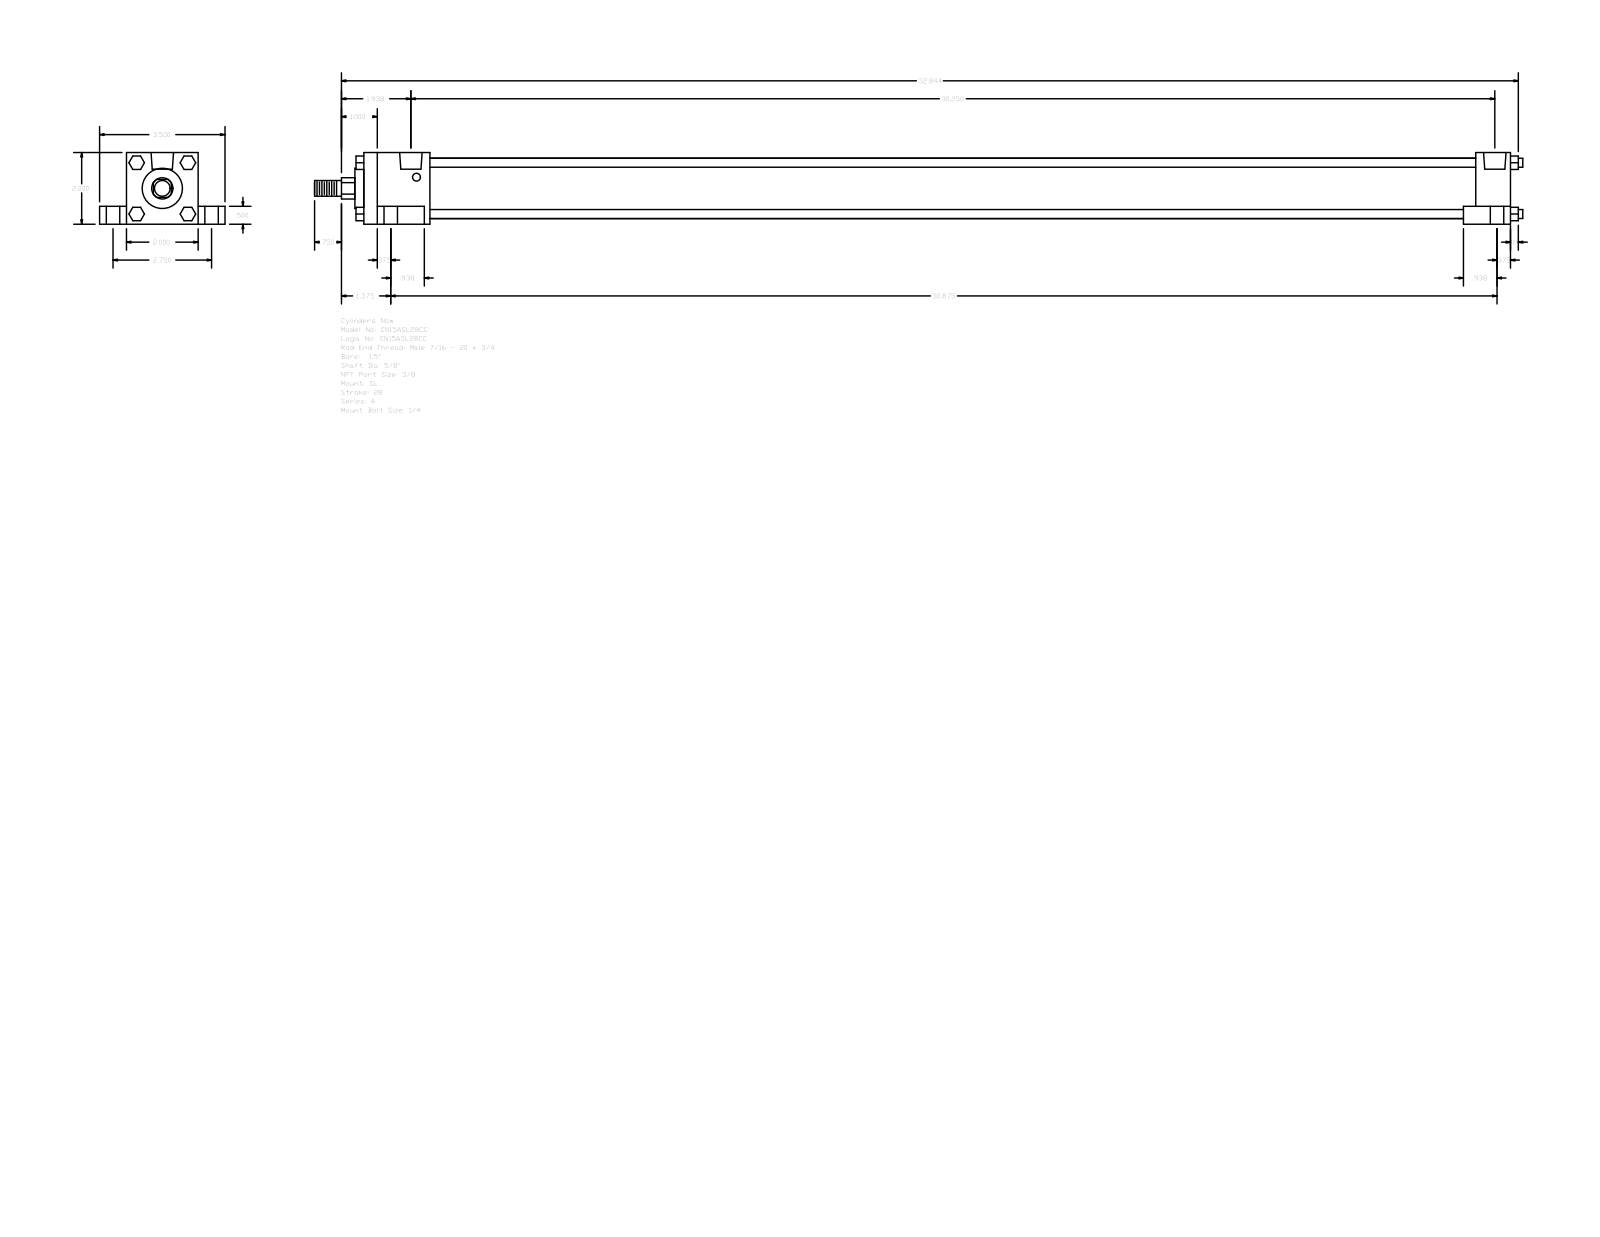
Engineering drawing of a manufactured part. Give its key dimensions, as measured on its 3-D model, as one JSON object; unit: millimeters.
{"part_name": "A_SL__0150_0.625", "step_written_by": "GSSL Pune (CONFIG_CONTROL_DESIGN)", "units": "millimeters", "bodies": {"solids": 0, "faces": 148, "planar": 112, "cylindrical": 36, "other": 0}, "overall_size": [856.46, 88.9, 50.8], "round_holes": [[5.56, 4], [9.53, 4], [15.88, 4], [15.93, 2]], "round_bosses_or_shafts": [[6.35, 4], [42.93, 1], [28.57, 1], [15.88, 1], [11.11, 1]], "partial_cylinders_radius": [[7.54, 1]], "face_to_face_distances": [50.8, 19.05, 38.1, 12.7, 69.85, 812.79, 9.52, 788.19, 24.6, 46.83], "hole_center_spacings": [3.97, 34.96, 35.36, 37.73, 39.41, 69.84, 760.41, 764.38]}
